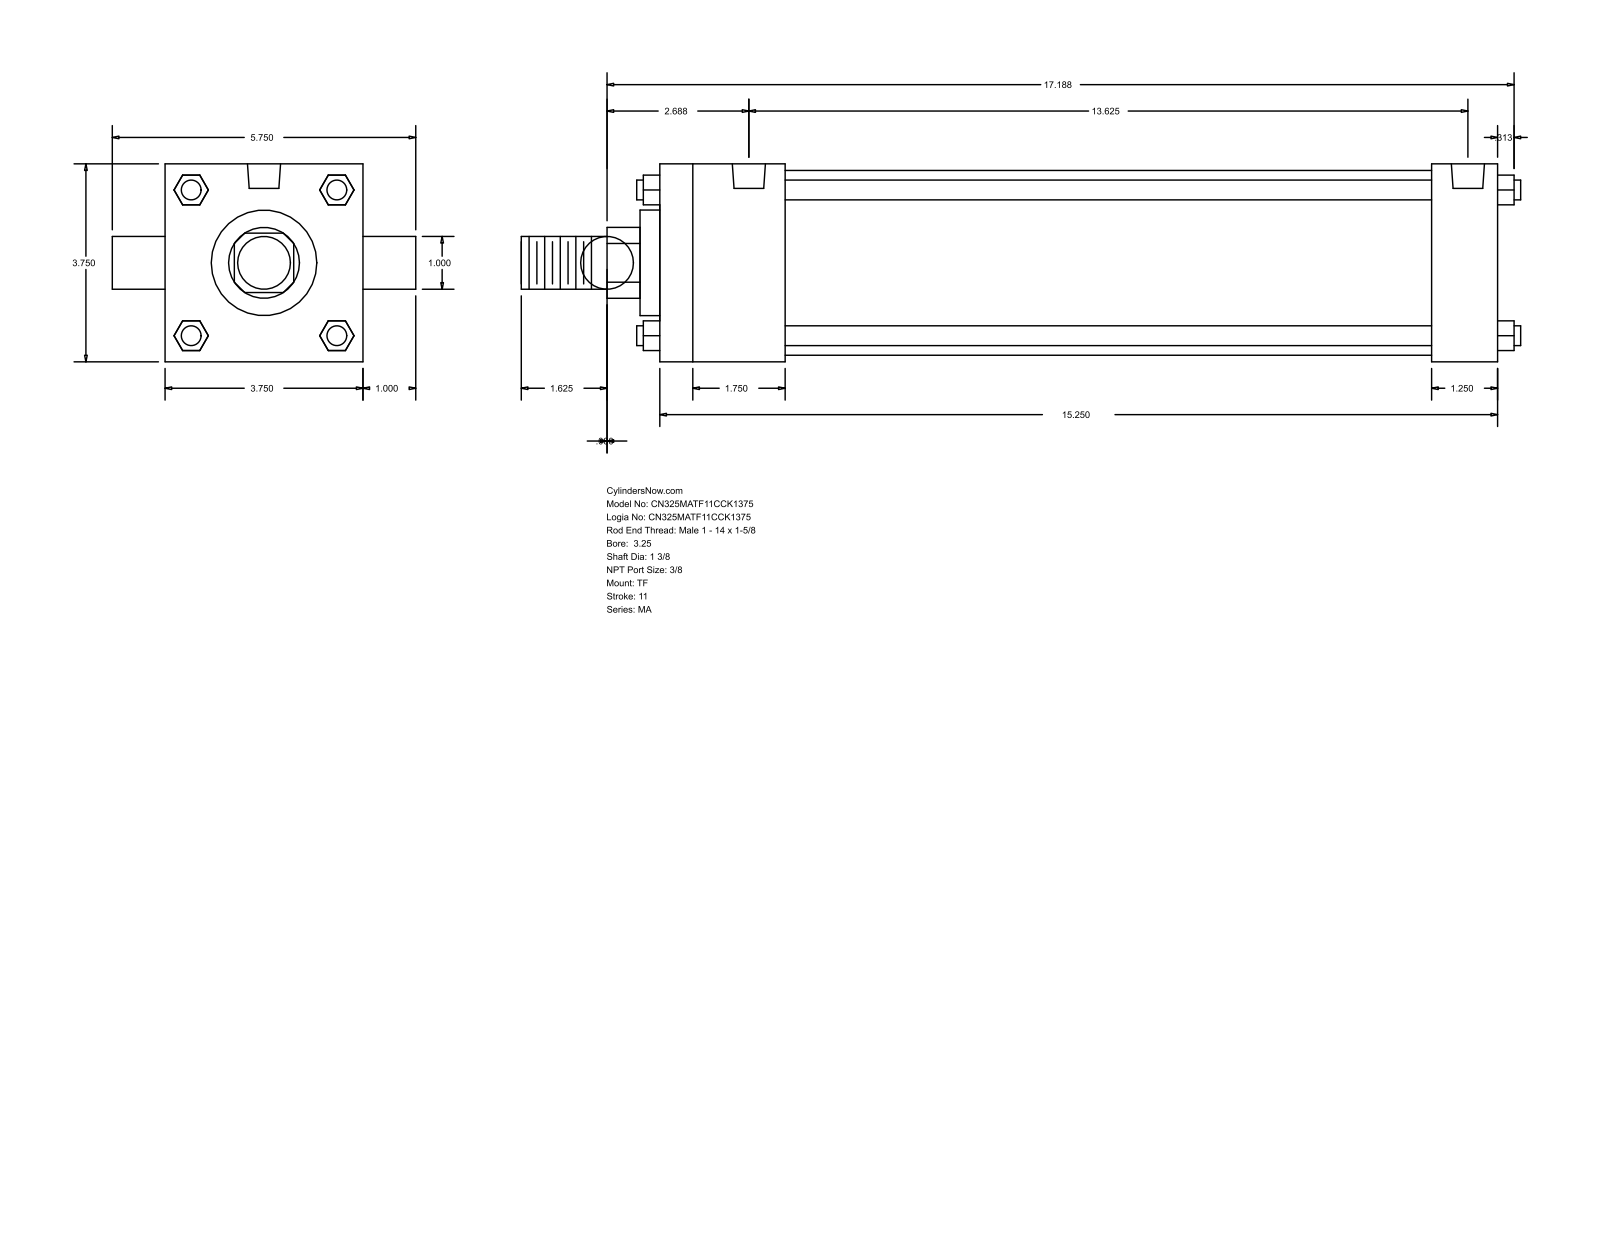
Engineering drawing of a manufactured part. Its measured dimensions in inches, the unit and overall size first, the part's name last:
Units: inches
Overall size (bounding box): 18.937 × 5.75 × 3.75
Round holes (diameter × count): ⌀0.437 ×3, ⌀0.627 ×2
Round bosses / shafts (diameter × count): ⌀0.375 ×4, ⌀1 ×2, ⌀3.5 ×1, ⌀2 ×1, ⌀1.375 ×1
Partial cylindrical surfaces — rounded edges, fillets, slot ends (radius × count): R0.672 ×1
Main face-to-face distances: 3.75, 15.875, 2.375, 14.625, 12.25, 13.5, 1.25, 0.375, 2.75, 15
Hole centre spacings: 0.188, 13.437, 13.25, 13.625
Bodies: 0 solids, 120 faces (92 planar, 28 cylindrical, 0 other)
Part name (STEP PRODUCT): MA_TF__0325_1.375
STEP written by: GSSL Pune (CONFIG_CONTROL_DESIGN)
